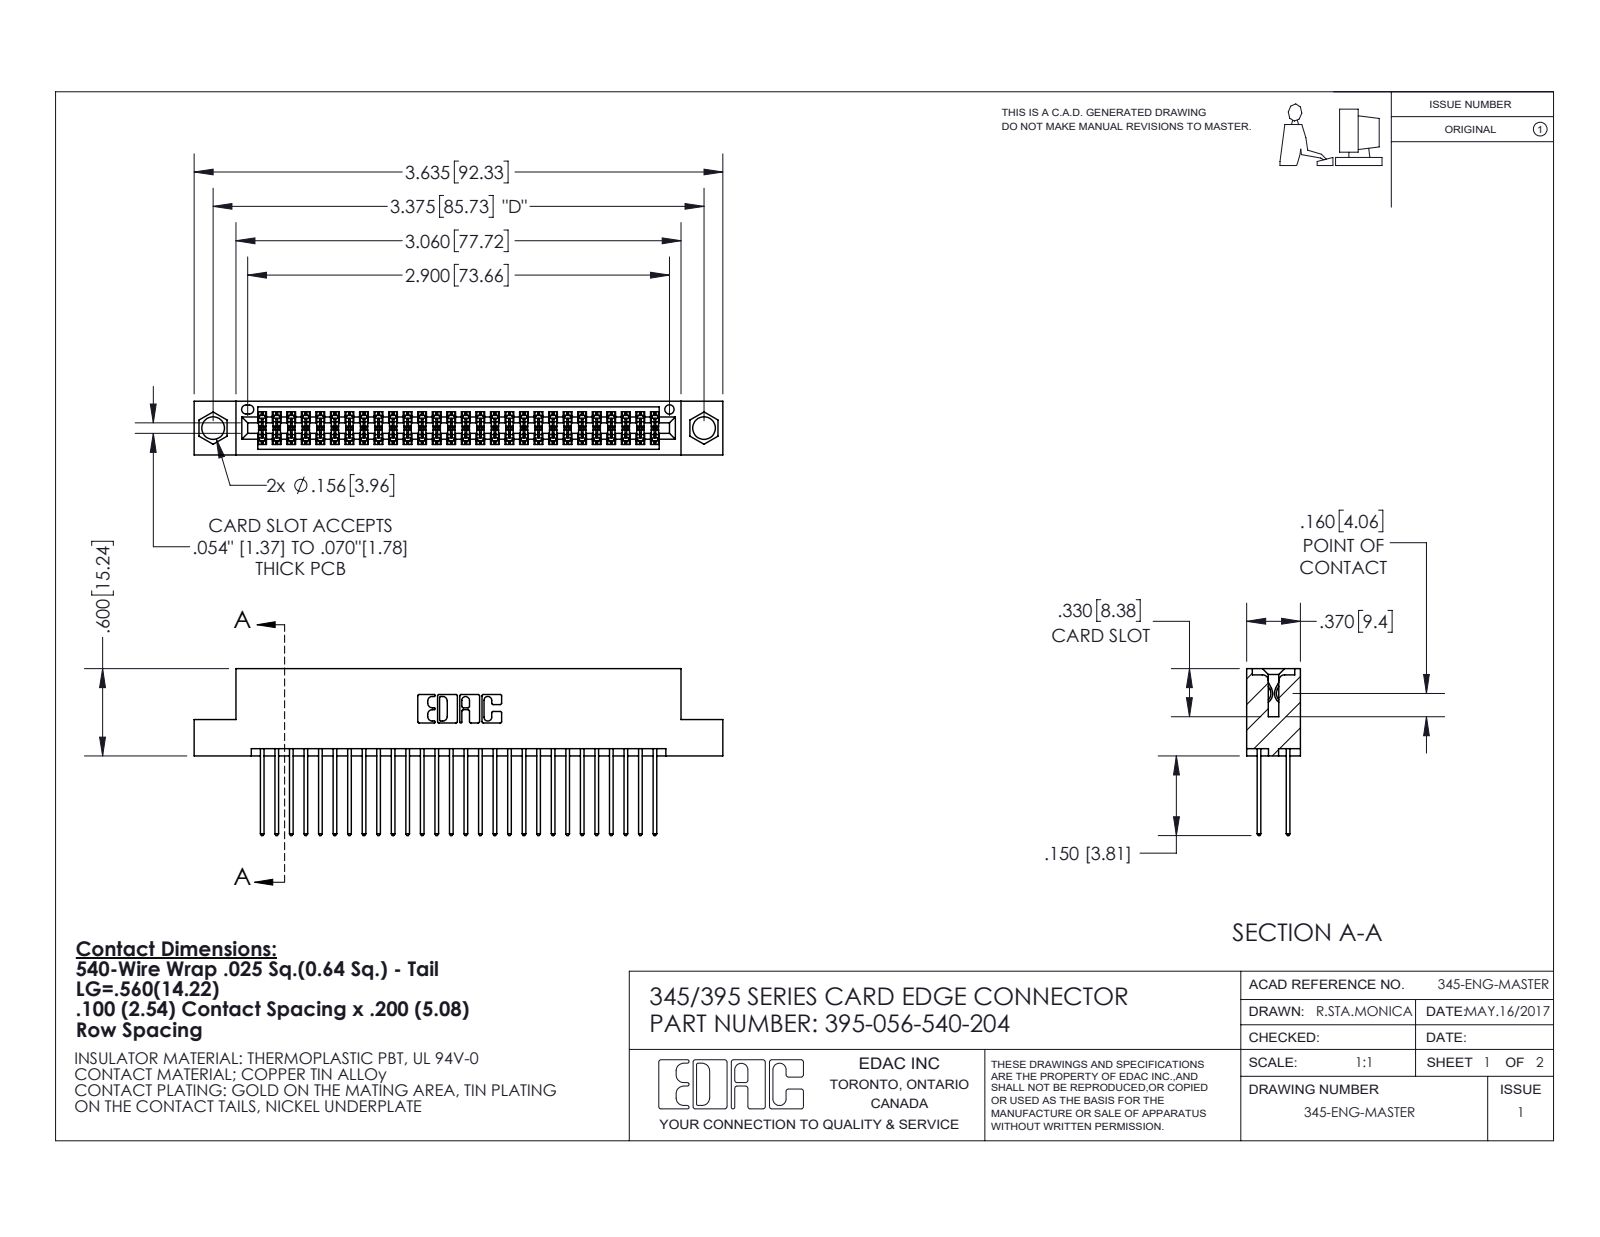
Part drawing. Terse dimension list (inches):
name: 345-292-001_345-293-140; 345 Part_Flush Mounting Lugs - 0.156 Dia-TI; 395-056-540-204
written by: SolidWorks 2020 (CONFIG_CONTROL_DESIGN)
unit: in
bodies: 57 solids, 2940 faces (1942 planar, 998 cylindrical, 0 other)
size: 3.635 × 1.147 × 0.37
volume: 0.546 in³; area: 21.37 in²
holes: 2× ⌀0.156, 1× ⌀0.064
rounds: 112× R0.006, 56× R0.01, 22× R0.01, 6× R0.007, 6× R0.031, 3× R0.026, 2× R0.014, 2× R0.019
face distances: 0.072, 0.298, 0.2, 0.098, 0.272, 0.025, 0.37, 0.225, 0.175, 0.149
hole spacings: 0.27, 3.14, 3.375
